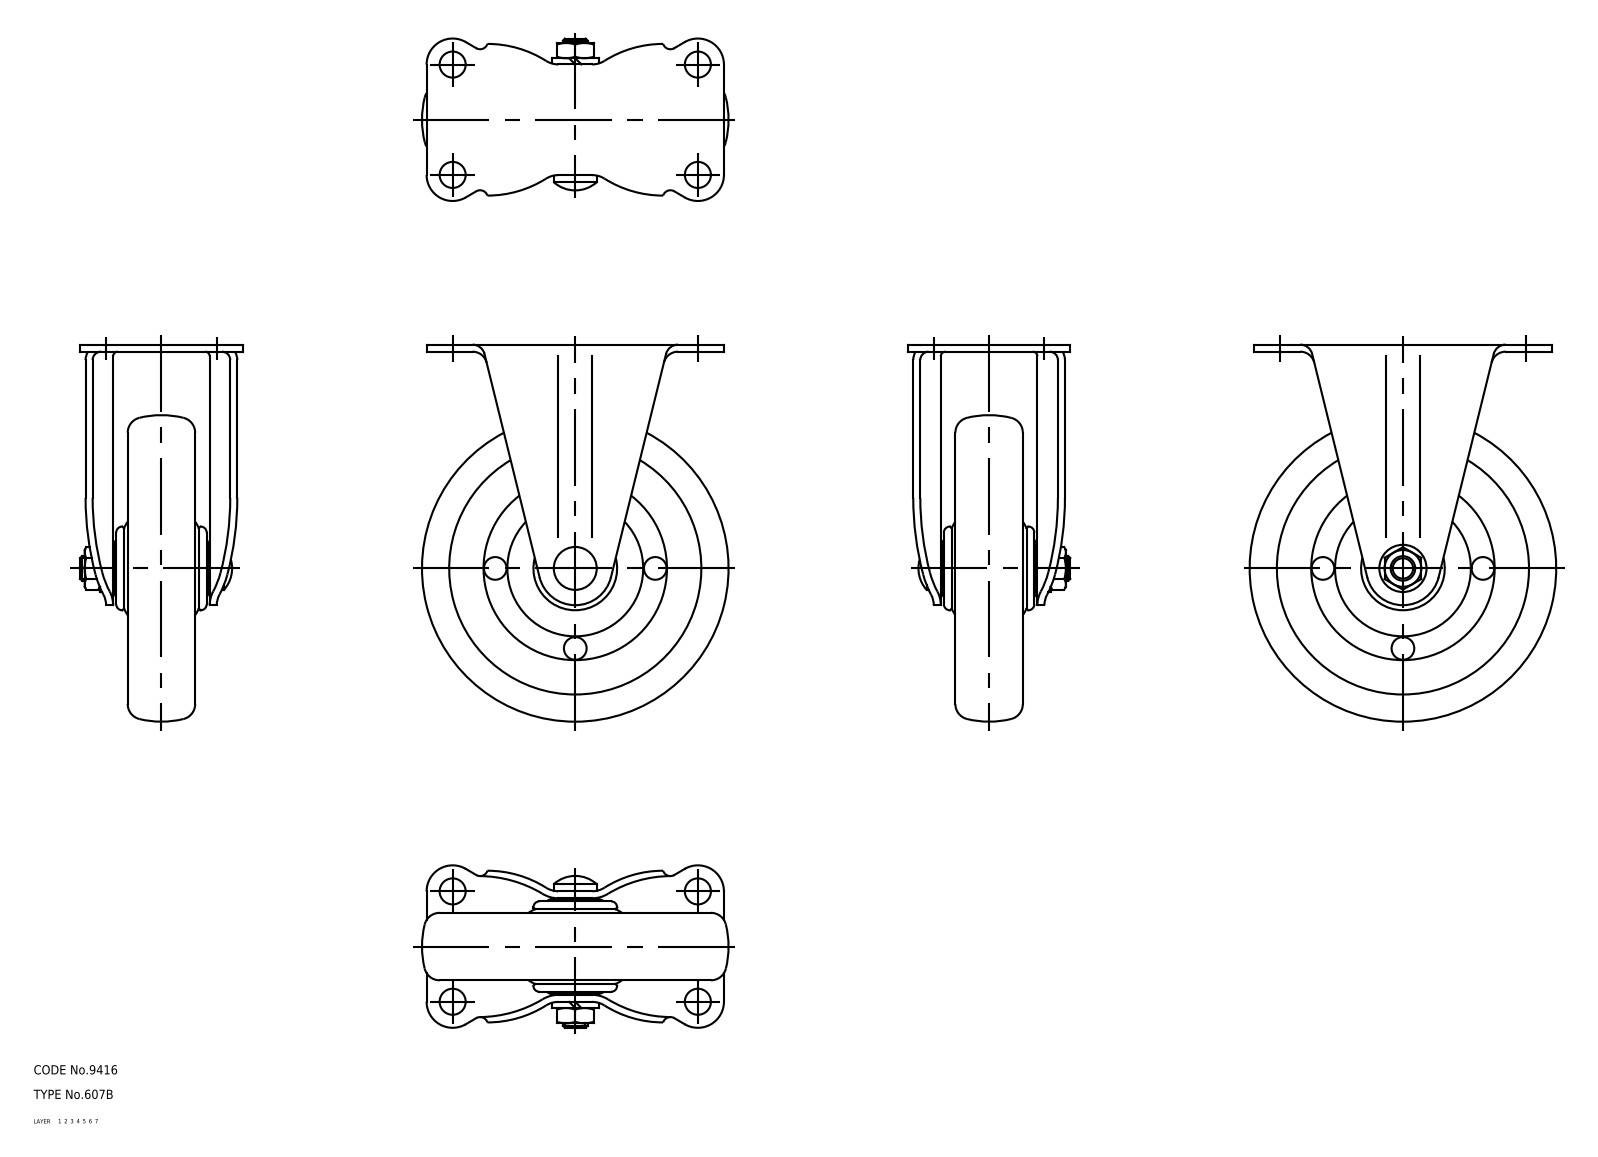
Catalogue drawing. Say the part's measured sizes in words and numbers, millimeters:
The part is named "wheel; axle; No_607B_17170_36". Its 3-D file was written by "CADfix (AUTOMOTIVE_DESIGN)". It is 3 solids with 198 faces: 0 planar, 0 cylindrical and 198 other. Overall it measures 123 by 100 by 53 millimeters. Its volume is 172 172 cubic millimeters and its surface area 48 218 square millimeters.
